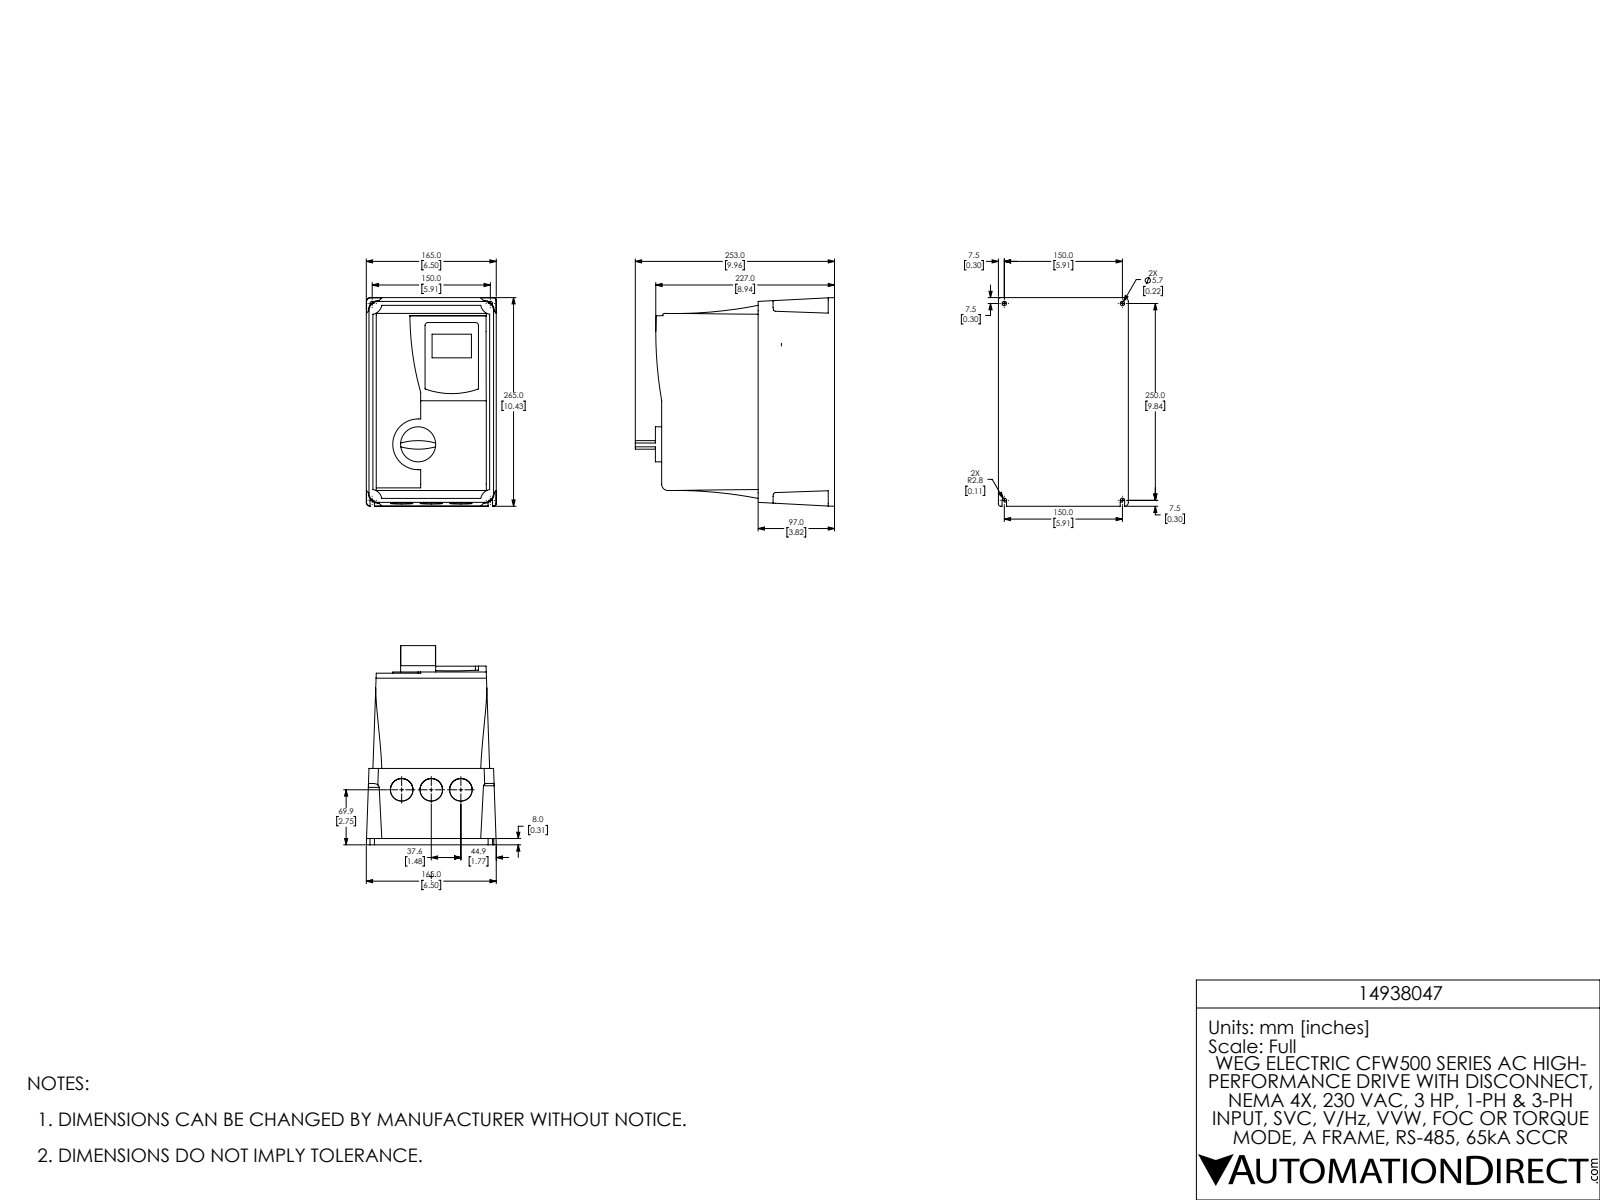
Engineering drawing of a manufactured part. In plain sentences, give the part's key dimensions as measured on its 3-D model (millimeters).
The part is named "CFW500 MEC-A IP66 - COM SECCIONADORA Coord". Its 3-D file was written by "SolidWorks 2017 (AUTOMOTIVE_DESIGN)". It is 1 solid with 93 faces: 47 planar, 45 cylindrical and 1 other. Overall it measures 265 by 253 by 165 millimeters. Its volume is 8 117 000 cubic millimeters and its surface area 257 400 square millimeters. Round holes: 3 of diameter 28.6, 2 of diameter 5.7. Round bosses or shafts: 1 of diameter 44.5. Partial cylindrical surfaces (rounded edges, fillets, slot ends): 4 of radius 3, 4 of radius 12, 4 of radius 14, 3 of radius 5, 2 of radius 0.8, 2 of radius 2.8, 2 of radius 3.9, 2 of radius 82. The main face-to-face distances are 5, 219.5, 218, 1.5, 97, 121, 122.5, 8, 275.7, 275.7. The hole center spacings are 37.6, 75.2, 150.
